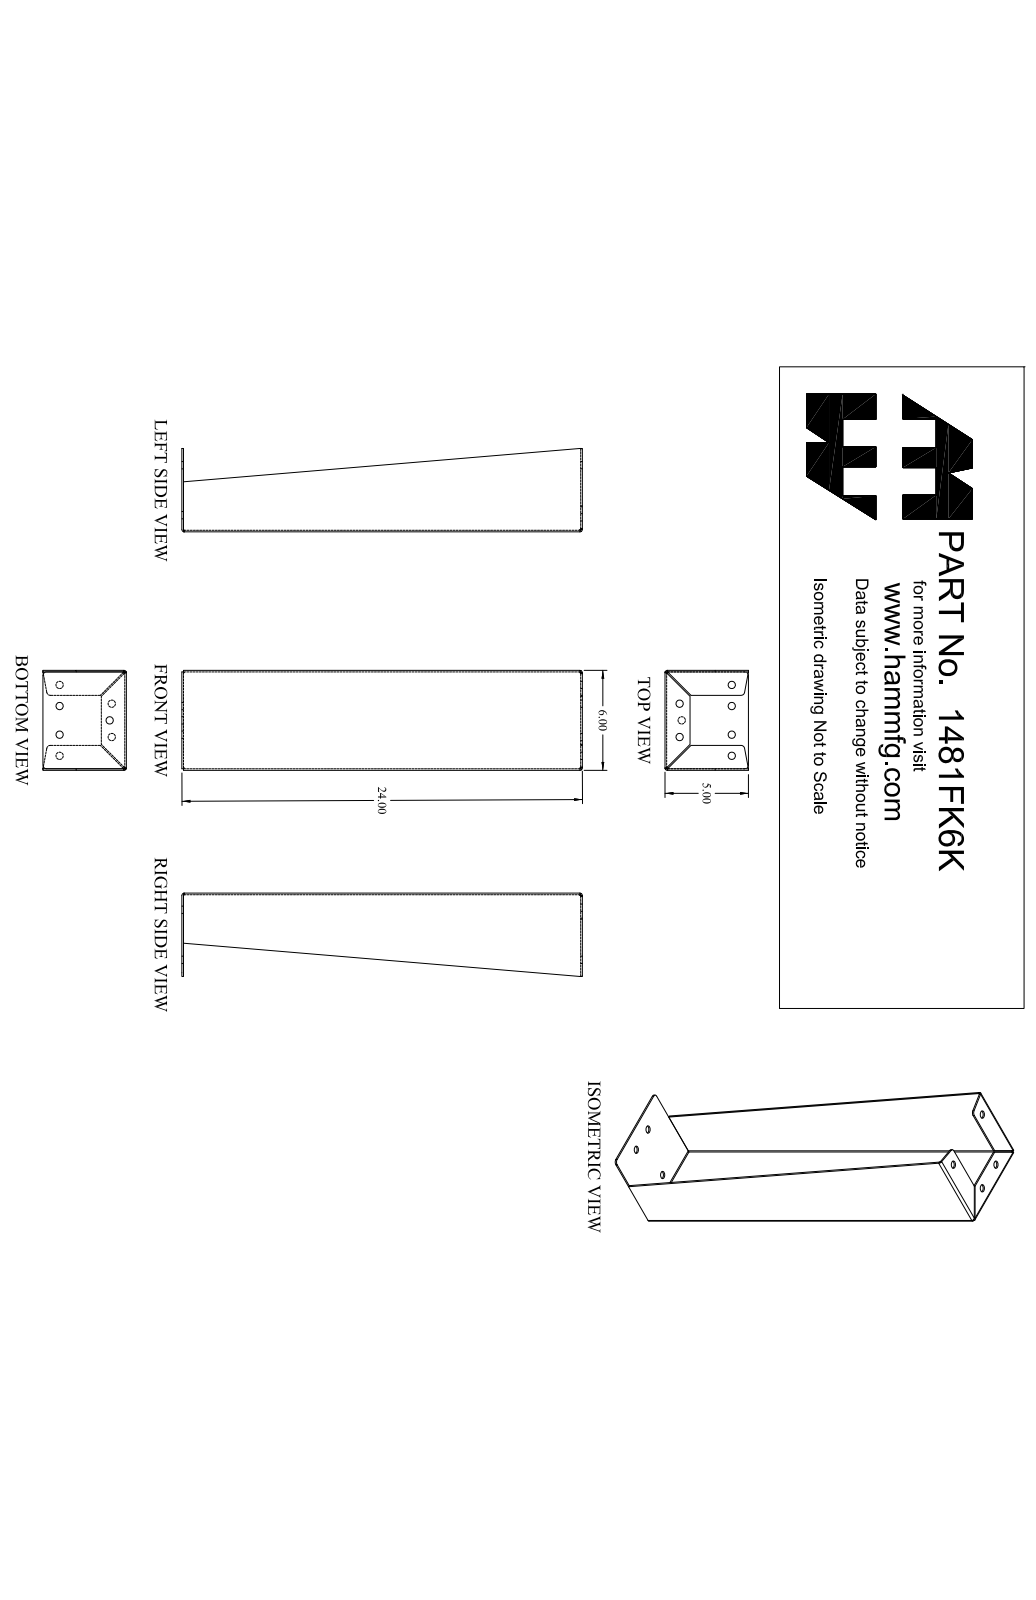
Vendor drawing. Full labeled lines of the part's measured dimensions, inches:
Part name (STEP PRODUCT): 1481FK6K_Default
STEP written by: SolidWorks 2019 (CONFIG_CONTROL_DESIGN)
Units: inches
Bodies: 1 solid, 78 faces (42 planar, 30 cylindrical, 6 other)
Overall size (bounding box): 24 × 6 × 5
Volume: 35.42 in³ · Surface area: 755.3 in²
Round holes (diameter × count): ⌀0.437 ×7
Partial cylindrical surfaces — rounded edges, fillets, slot ends (radius × count): R0.048 ×6, R0.143 ×6, R0.22 ×4
Main face-to-face distances: 0.095, 5.905, 6, 5.81, 0.095, 23.81, 23.905, 23.905, 24, 1.405
Hole centre spacings: 1.008, 3.12, 3.128, 3.321, 3.636, 4.419, 1.266, 1.266
